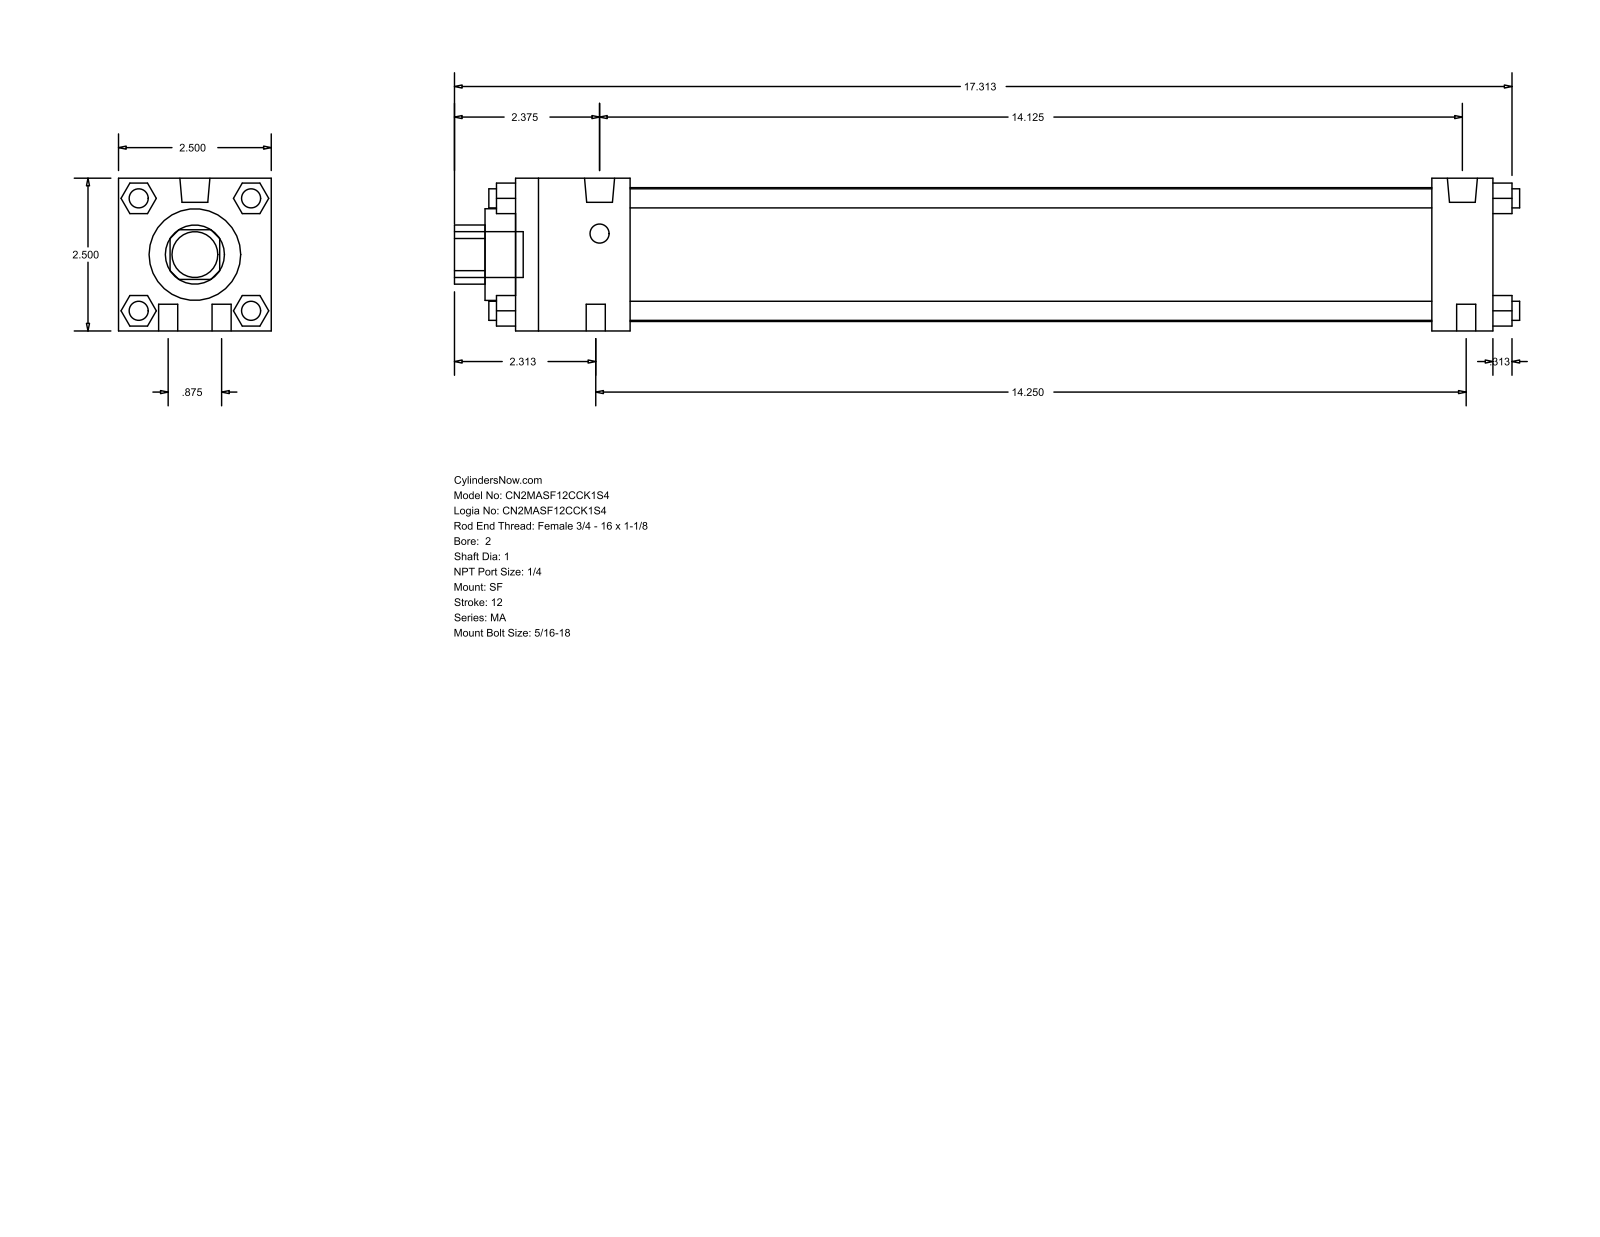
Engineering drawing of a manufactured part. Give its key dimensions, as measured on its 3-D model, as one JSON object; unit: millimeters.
{"part_name": "MA_SF__0200_1", "step_written_by": "GSSL Pune (CONFIG_CONTROL_DESIGN)", "units": "millimeters", "bodies": {"solids": 0, "faces": 124, "planar": 94, "cylindrical": 30, "other": 0}, "overall_size": [442.91, 63.5, 63.5], "round_holes": [[25.4, 1], [38.1, 1], [55.63, 1]], "round_bosses_or_shafts": [[7.94, 10], [12.49, 2], [19.05, 1]], "partial_cylinders_radius": [[12.29, 1]], "face_to_face_distances": [63.5, 406.4, 12.7, 25.4, 381, 47.63, 333.37, 358.77, 40.47, 23.37]}
